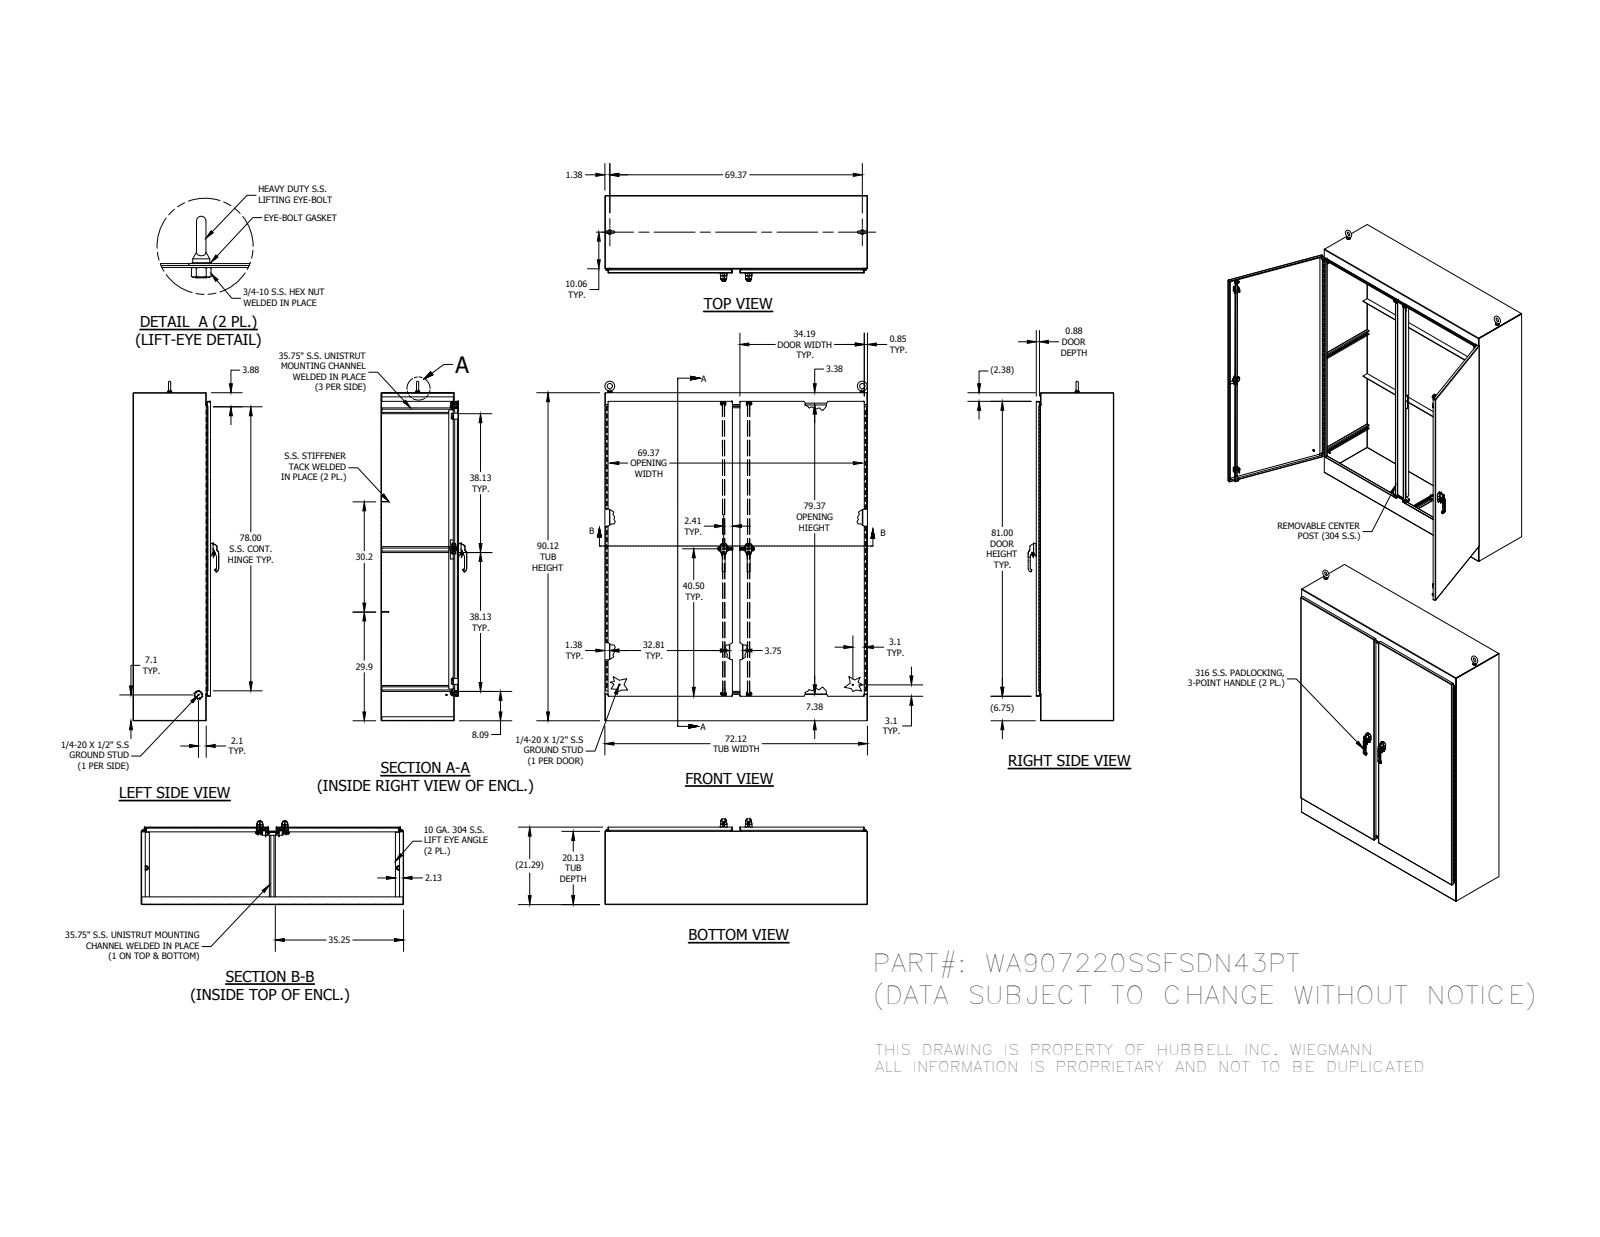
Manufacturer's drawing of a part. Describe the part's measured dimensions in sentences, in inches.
The part is named "1091-903_AF0; WA9072SSFSDN43PTRDR; SUPPORT-ROLL_AF0; 328131T-78 (+8 more)". Its 3-D file was written by "SolidWorks 2014 (AUTOMOTIVE_DESIGN)". It is 133 solids with 7276 faces: 2800 planar, 2780 cylindrical and 1696 other. Overall it measures 93.248 by 72.125 by 23.541 inches. Its volume is 2 882 cubic inches and its surface area 46 948 square inches. Round holes: 16 of diameter 0.262, 16 of diameter 0.375, 8 of diameter 0.187, 6 of diameter 0.213, 6 of diameter 0.25, 6 of diameter 0.281, 4 of diameter 0.196, 4 of diameter 0.241, 4 of diameter 0.252, 4 of diameter 0.281, 4 of diameter 0.315, 4 of diameter 0.4. Round bosses or shafts: 7 of diameter 0.25, 6 of diameter 1, 6 of diameter 0.533, 6 of diameter 0.236, 4 of diameter 0.563, 4 of diameter 0.531, 4 of diameter 0.5, 4 of diameter 0.438. Partial cylindrical surfaces (rounded edges, fillets, slot ends): 350 of radius 0.02, 213 of radius 0.012, 44 of radius 0.019, 44 of radius 0.125, 34 of radius 0.05, 28 of radius 0.079, 24 of radius 0.025, 24 of radius 0.059. The main face-to-face distances are 0.125, 0.125, 21.167, 72, 21.165, 21.04, 21.042, 90, 21.29, 21.165. The hole center spacings are 72.49, 73.24, 26, 0.38, 0.38, 8.667, 0.76, 17.333.
